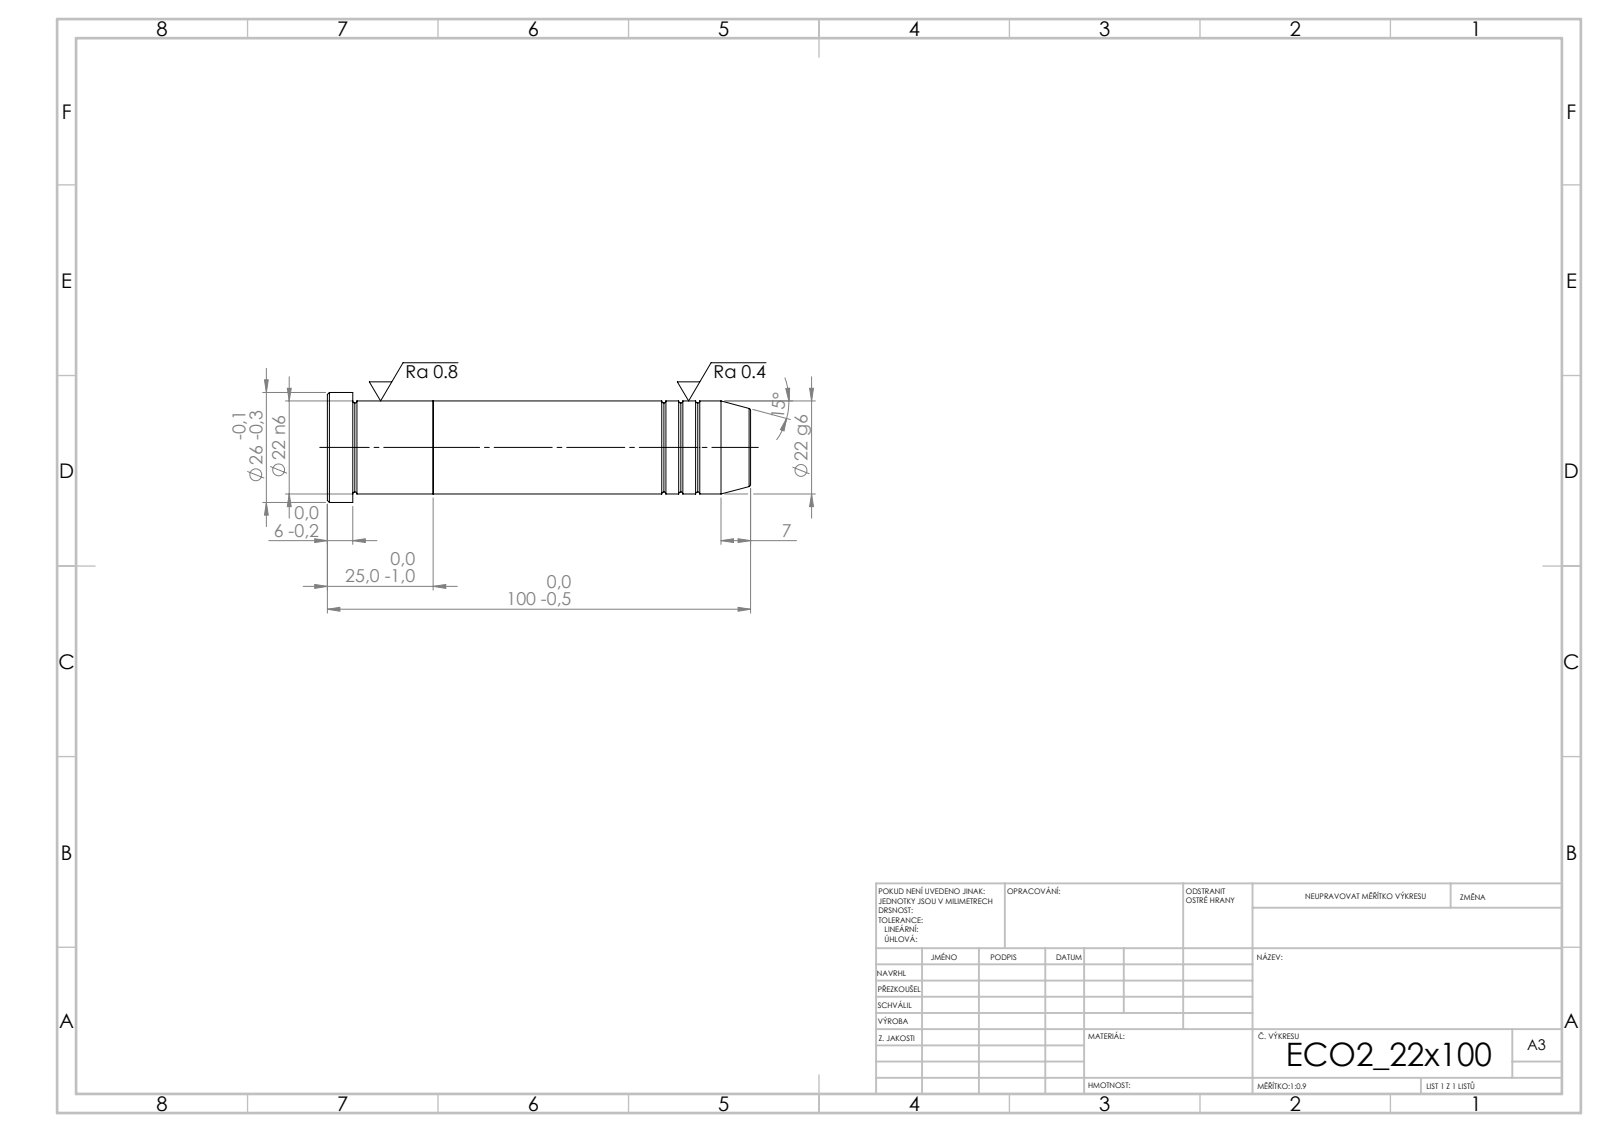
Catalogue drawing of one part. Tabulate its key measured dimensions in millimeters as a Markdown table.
| quantity | value |
| --- | --- |
| STEP written by | SolidWorks 2019 (CONFIG_CONTROL_DESIGN) |
| units | millimeters |
| bodies | 2 solids, 39 faces (5 planar, 12 cylindrical, 22 other) |
| overall size | 100 × 26 × 26 |
| volume | 38 372 mm³ |
| surface area | 8 779 mm² |
| round bosses / shafts (diameter × count) | 26 × 1, 22 × 1 |
| main face-to-face distances | 25, 75, 100, 94, 19, 6 |
